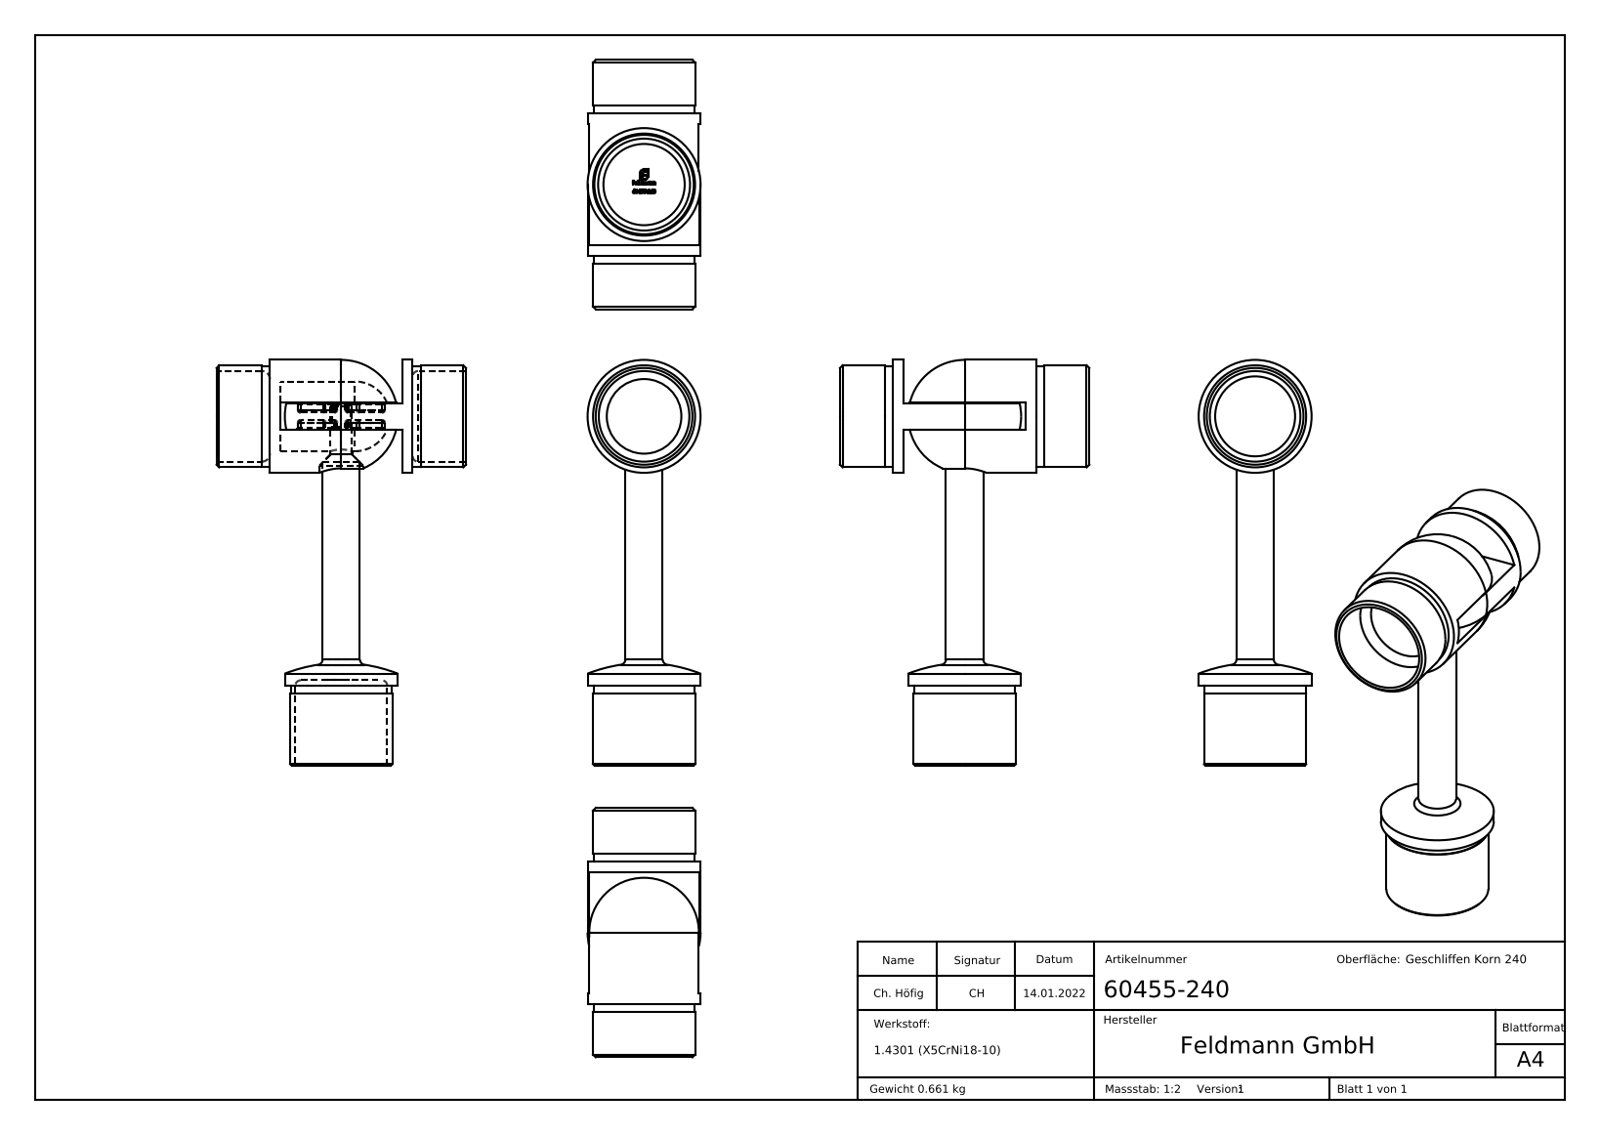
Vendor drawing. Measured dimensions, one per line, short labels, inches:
name: 60455-240 Teil1; 60455-240 Teil2_60455-240 Teil2; 60455-240 Teil1_60455-240 Teil1; 60455-240 (+3 more)
written by: SolidWorks 2018 (CONFIG_CONTROL_DESIGN)
unit: in
bodies: 3 solids, 501 faces (199 planar, 101 cylindrical, 201 other)
size: 5.995 × 3.685 × 1.669
volume: 5.108 in³; area: 66.28 in²
holes: 1× ⌀0.268, 1× ⌀0.323, 1× ⌀0.65, 1× ⌀1.299, 1× ⌀1.339, 1× ⌀1.358
bosses: 2× ⌀1.669, 2× ⌀1.508, 2× ⌀1.492, 1× ⌀0.551, 1× ⌀0.315
rounds: 24× R0.039, 1× R0.246, 1× R0.516
face distances: 0.157, 1.953, 0.394, 2.11, 0.146, 0.256, 0.138, 0.248, 0.386, 3.708
